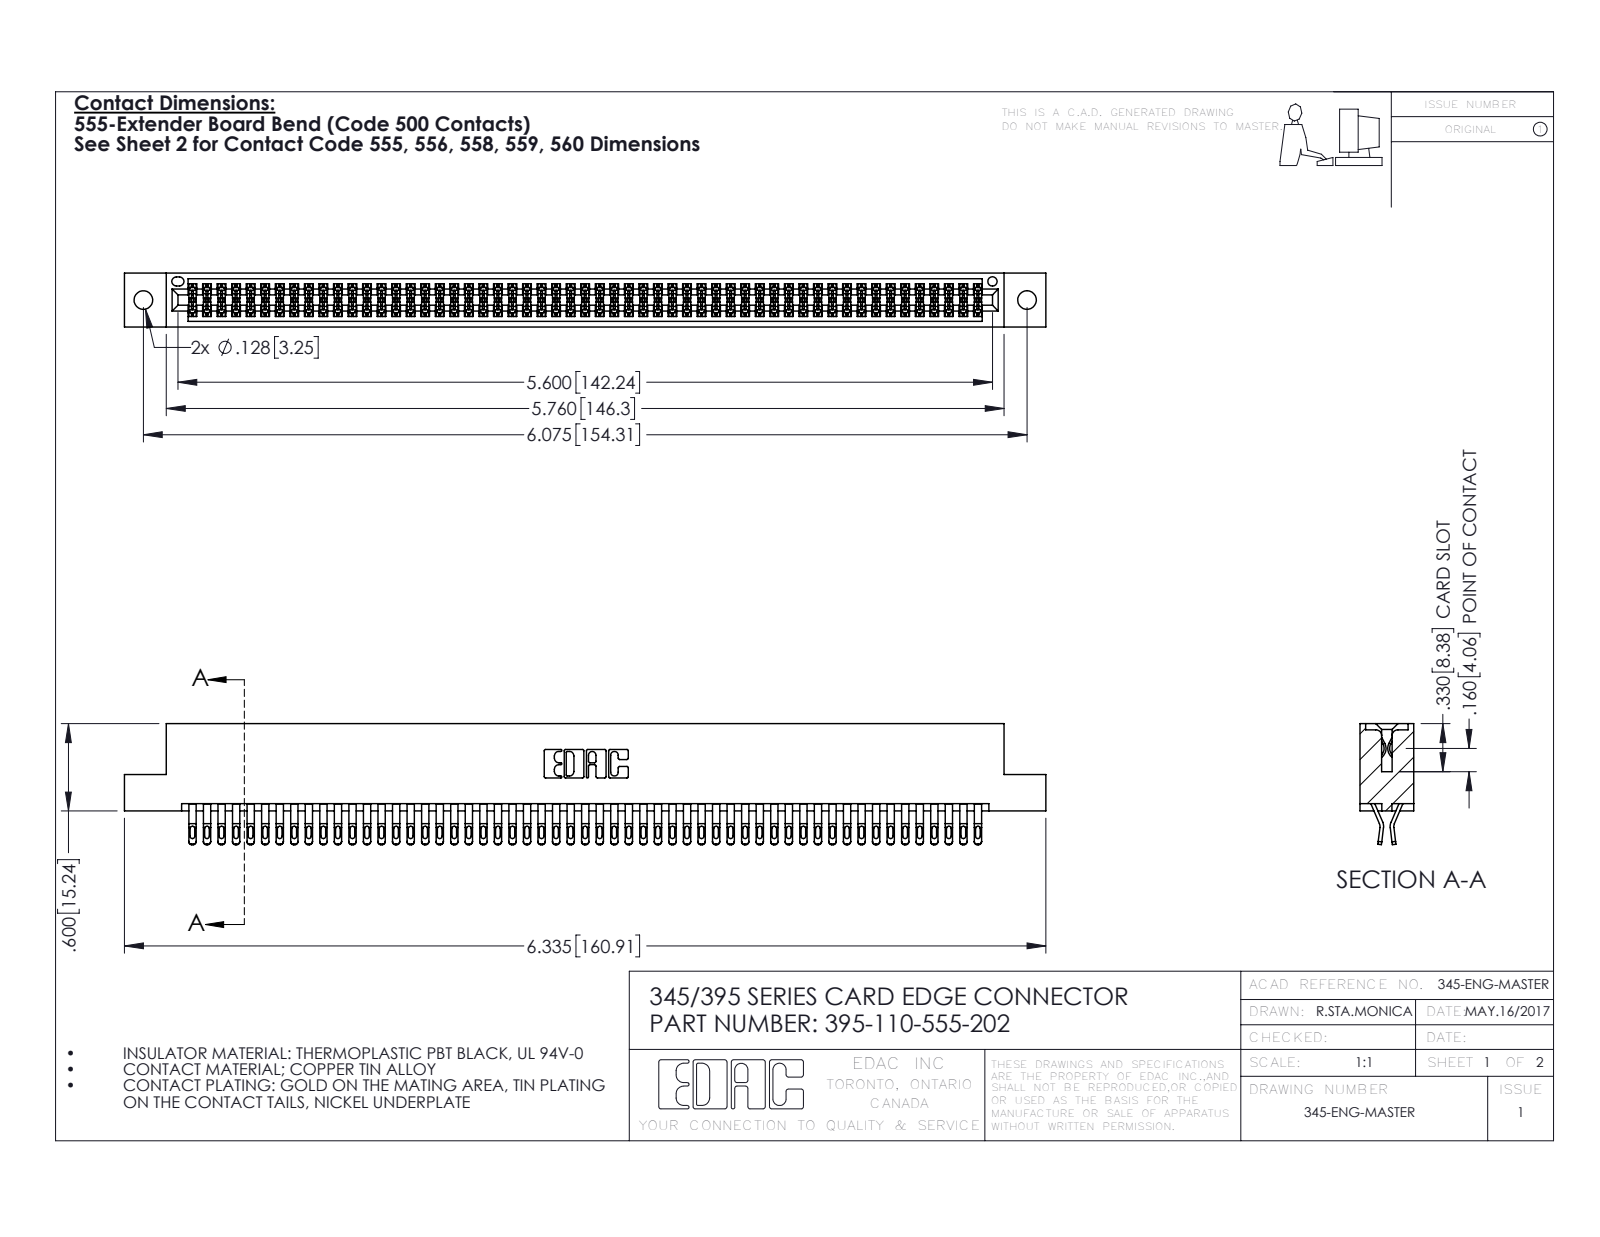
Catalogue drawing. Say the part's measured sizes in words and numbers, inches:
The part is named "345-292-001_555 Tail; 345 Part_Flush Mounting Lugs - 0.128 Dia; 395-110-555-202". Its 3-D file was written by "SolidWorks 2016 (CONFIG_CONTROL_DESIGN)". It is 111 solids with 6286 faces: 3490 planar, 2796 cylindrical and 0 other. Overall it measures 6.335 by 0.832 by 0.37 inches. Its volume is 0.978 cubic inches and its surface area 38.42 square inches. Round holes: 2 of diameter 0.128, 1 of diameter 0.064. Partial cylindrical surfaces (rounded edges, fillets, slot ends): 275 of radius 0.016, 220 of radius 0.02, 165 of radius 0.006, 22 of radius 0.01, 6 of radius 0.007, 6 of radius 0.031, 3 of radius 0.026, 2 of radius 0.01. The main face-to-face distances are 0.298, 0.072, 0.025, 0.37, 0.2, 0.098, 0.272, 0.225, 0.175, 0.149. The hole center spacings are 0.27, 5.839, 6.075.
